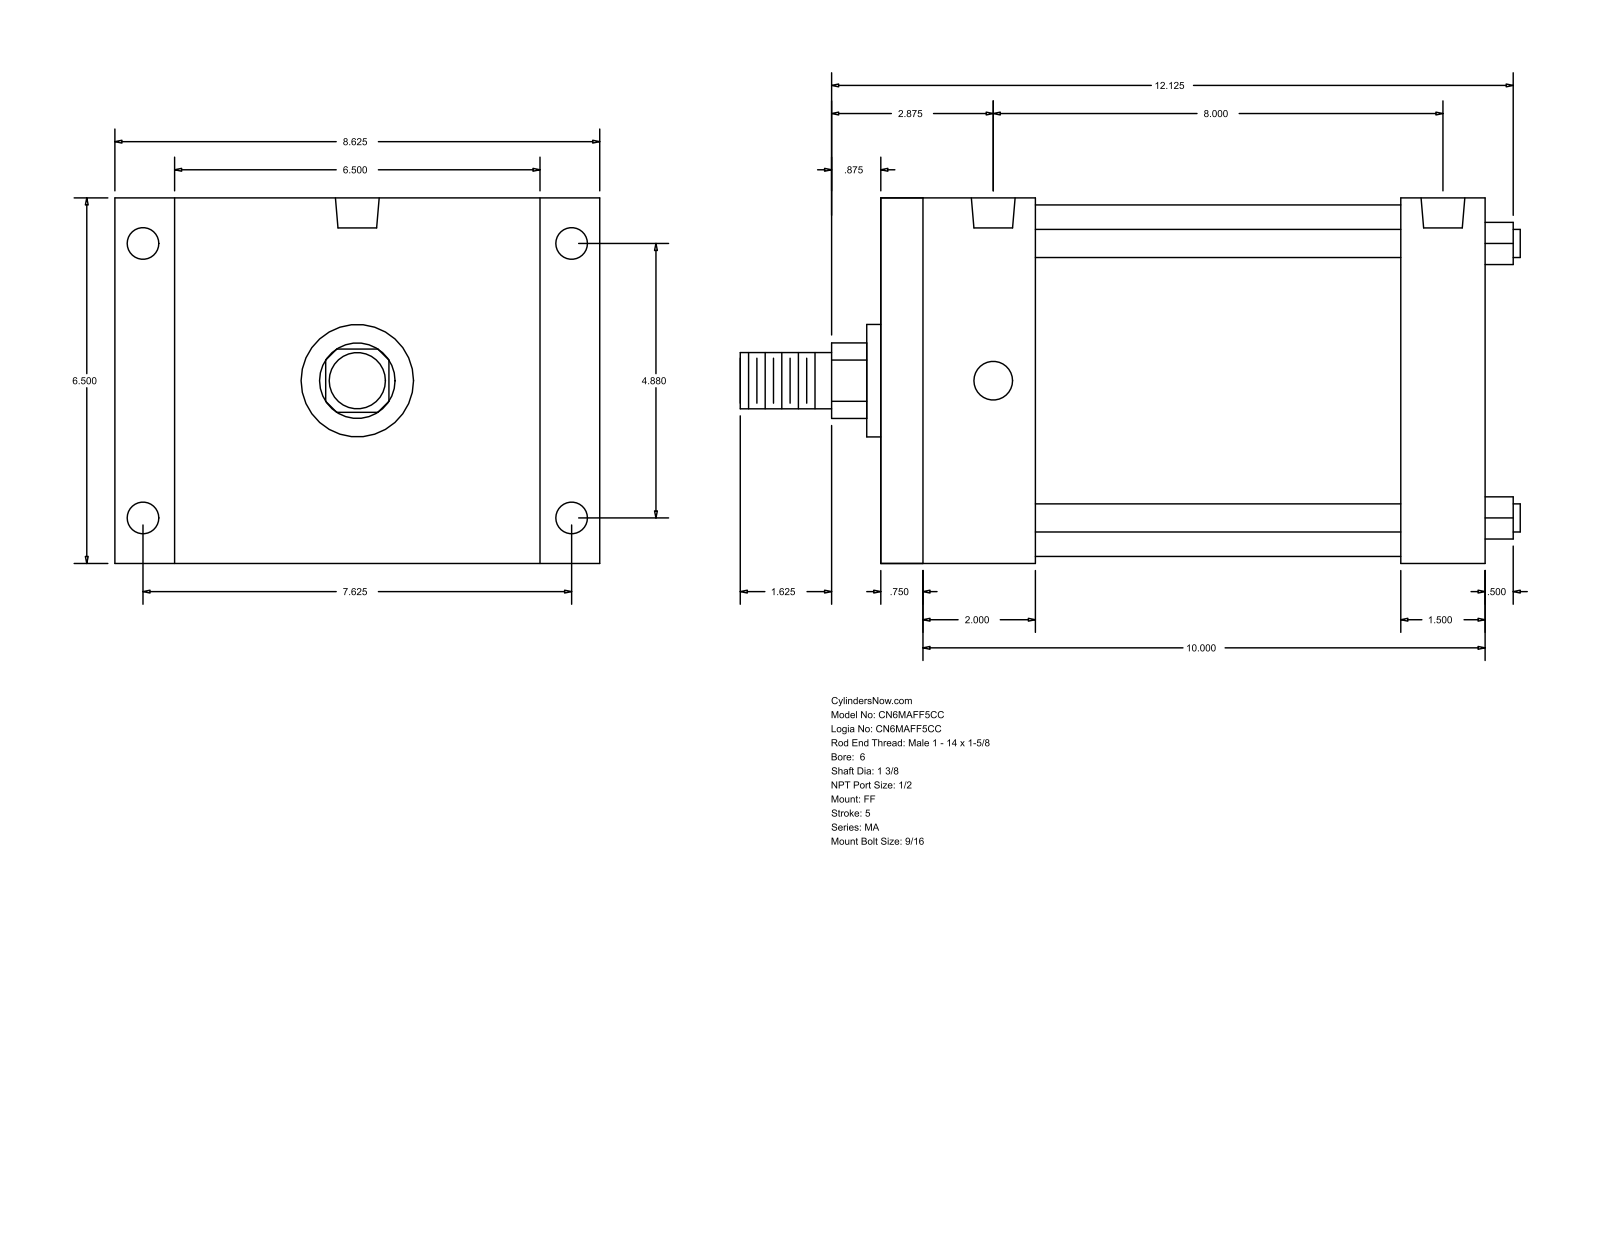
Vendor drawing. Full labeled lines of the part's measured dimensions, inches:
Part name (STEP PRODUCT): MA_FF__0600_1.375
STEP written by: GSSL Pune (CONFIG_CONTROL_DESIGN)
Units: inches
Bodies: 0 solids, 92 faces (64 planar, 28 cylindrical, 0 other)
Overall size (bounding box): 13.875 × 8.625 × 6.5
Round holes (diameter × count): ⌀0.563 ×4, ⌀0.687 ×4, ⌀0.778 ×2
Round bosses / shafts (diameter × count): ⌀0.5 ×4, ⌀6.25 ×1, ⌀2 ×1, ⌀1.375 ×1, ⌀1 ×1
Partial cylindrical surfaces — rounded edges, fillets, slot ends (radius × count): R0.672 ×1
Main face-to-face distances: 6.5, 10.75, 8.625, 0.625, 10.125, 2, 2.625, 8.125, 9.25, 6.625
Hole centre spacings: 4.88, 7.625, 8.125, 9.053, 0.125, 8
